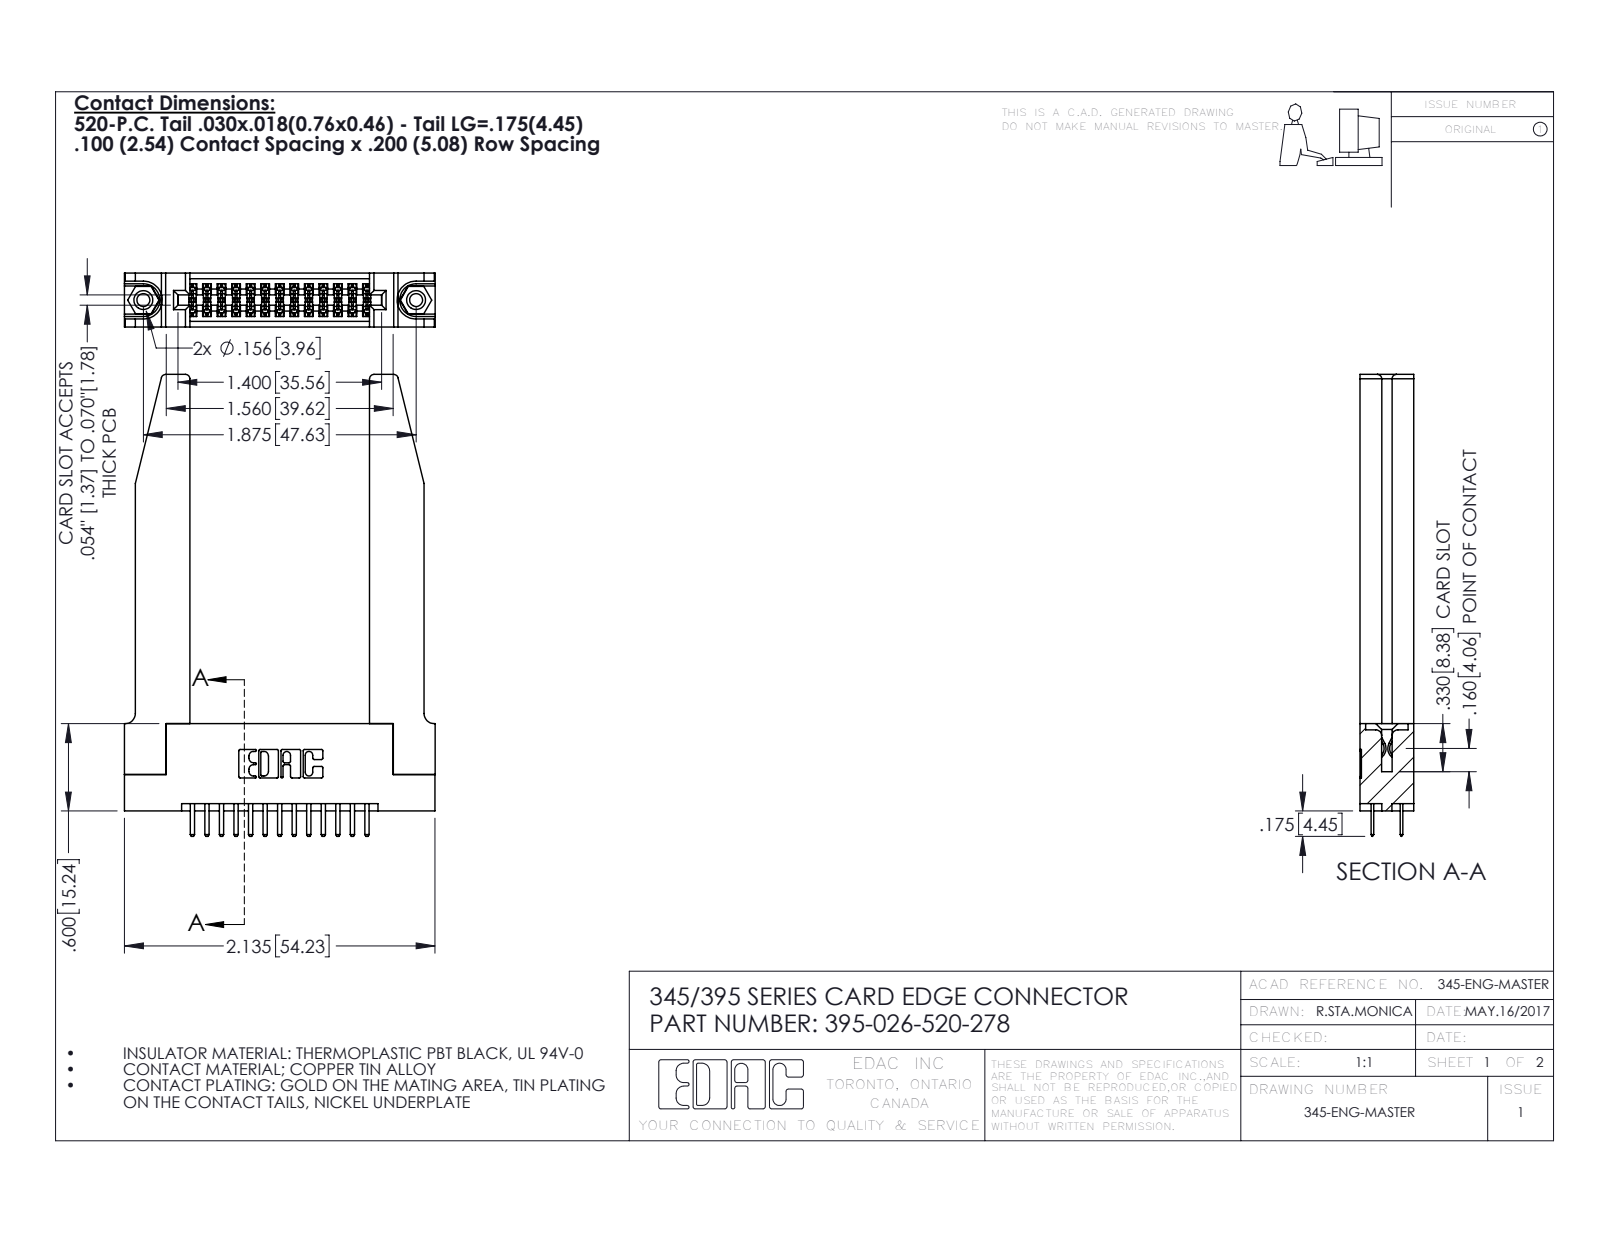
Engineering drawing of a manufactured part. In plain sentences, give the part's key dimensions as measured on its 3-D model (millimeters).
The part is named "345-220-078_345-220-078; 395-026-520-278; 345-250-001_345-250-001-102; 345 Part_Flush Mounting Lugs - 0.156 Dia-TH (+1 more)". Its 3-D file was written by "SolidWorks 2016 (CONFIG_CONTROL_DESIGN)". It is 31 solids with 1764 faces: 1132 planar, 580 cylindrical and 52 other. Overall it measures 80.6 by 54.3 by 9.4 millimeters. Its volume is 12 800 cubic millimeters and its surface area 13 630 square millimeters. Round holes: 2 of diameter 2.3, 2 of diameter 3.2, 2 of diameter 4, 1 of diameter 1.6. Round bosses or shafts: 2 of diameter 3.9. Partial cylindrical surfaces (rounded edges, fillets, slot ends): 39 of radius 0.2, 30 of radius 0.3, 22 of radius 0.3, 8 of radius 0.8, 6 of radius 0.2, 6 of radius 0.8, 3 of radius 0.7, 2 of radius 0.4. The main face-to-face distances are 9.4, 1.8, 7.6, 5.1, 2, 3.8, 5.6, 3.8, 31.4, 2.5. The hole center spacings are 6.9, 41.7, 47.6.
